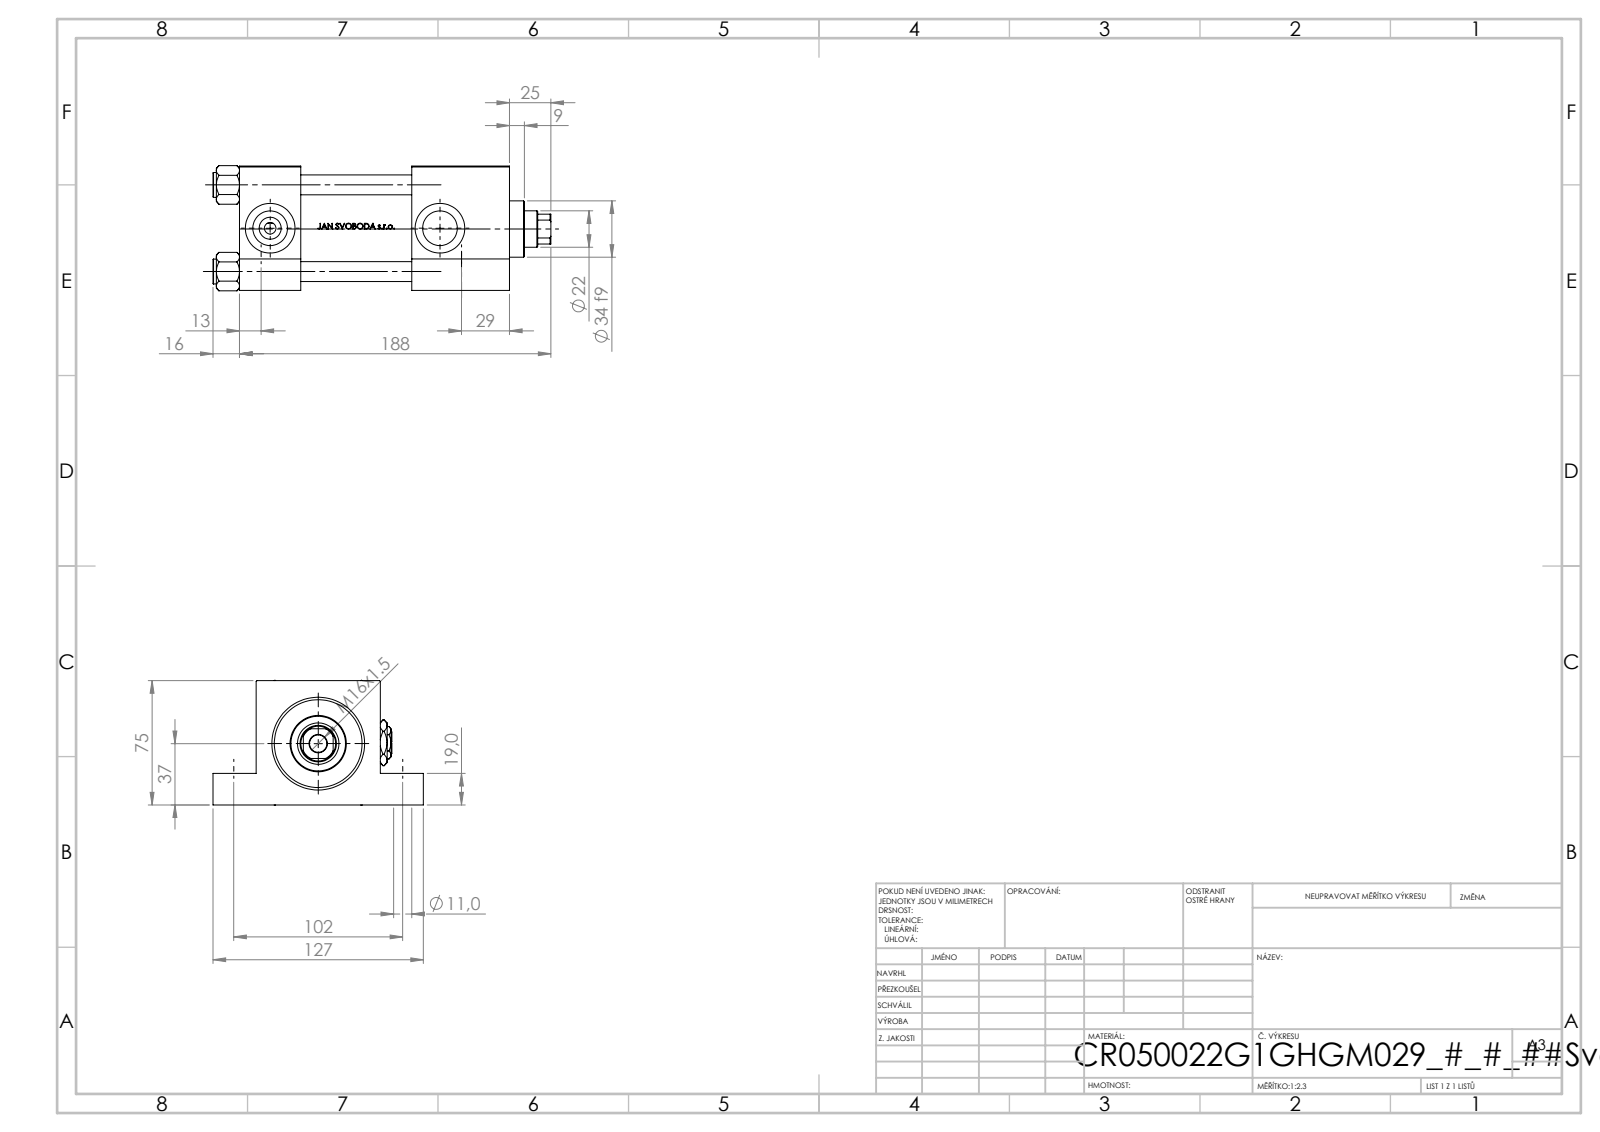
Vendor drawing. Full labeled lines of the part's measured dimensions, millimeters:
Part name (STEP PRODUCT): V215CR_G_Body; Zatka_pro_OIL_PORT; V215_VC_A; V215CR_VCP_G (+2 more)
STEP written by: SolidWorks 2019 (CONFIG_CONTROL_DESIGN)
Units: millimetres
Bodies: 12 solids, 1134 faces (454 planar, 128 cylindrical, 552 other)
Overall size (bounding box): 204 × 127 × 75.54
Volume: 764 391 mm³ · Surface area: 166 280 mm²
Round holes (diameter × count): ⌀11 ×4, ⌀12 ×4, ⌀7 ×2, ⌀20.96 ×2, ⌀30 ×2, ⌀10.5 ×1, ⌀22 ×1, ⌀25 ×1, ⌀41 ×1, ⌀50 ×1, ⌀53 ×1
Round bosses / shafts (diameter × count): ⌀15 ×4, ⌀56 ×1, ⌀34 ×1
Partial cylindrical surfaces — rounded edges, fillets, slot ends (radius × count): R10.5 ×1
Main face-to-face distances: 75, 37, 163, 126, 19, 56, 104, 67, 59, 26
Hole centre spacings: 52.3, 36.63, 37.34, 73.96, 102, 121, 158.26, 102.5
